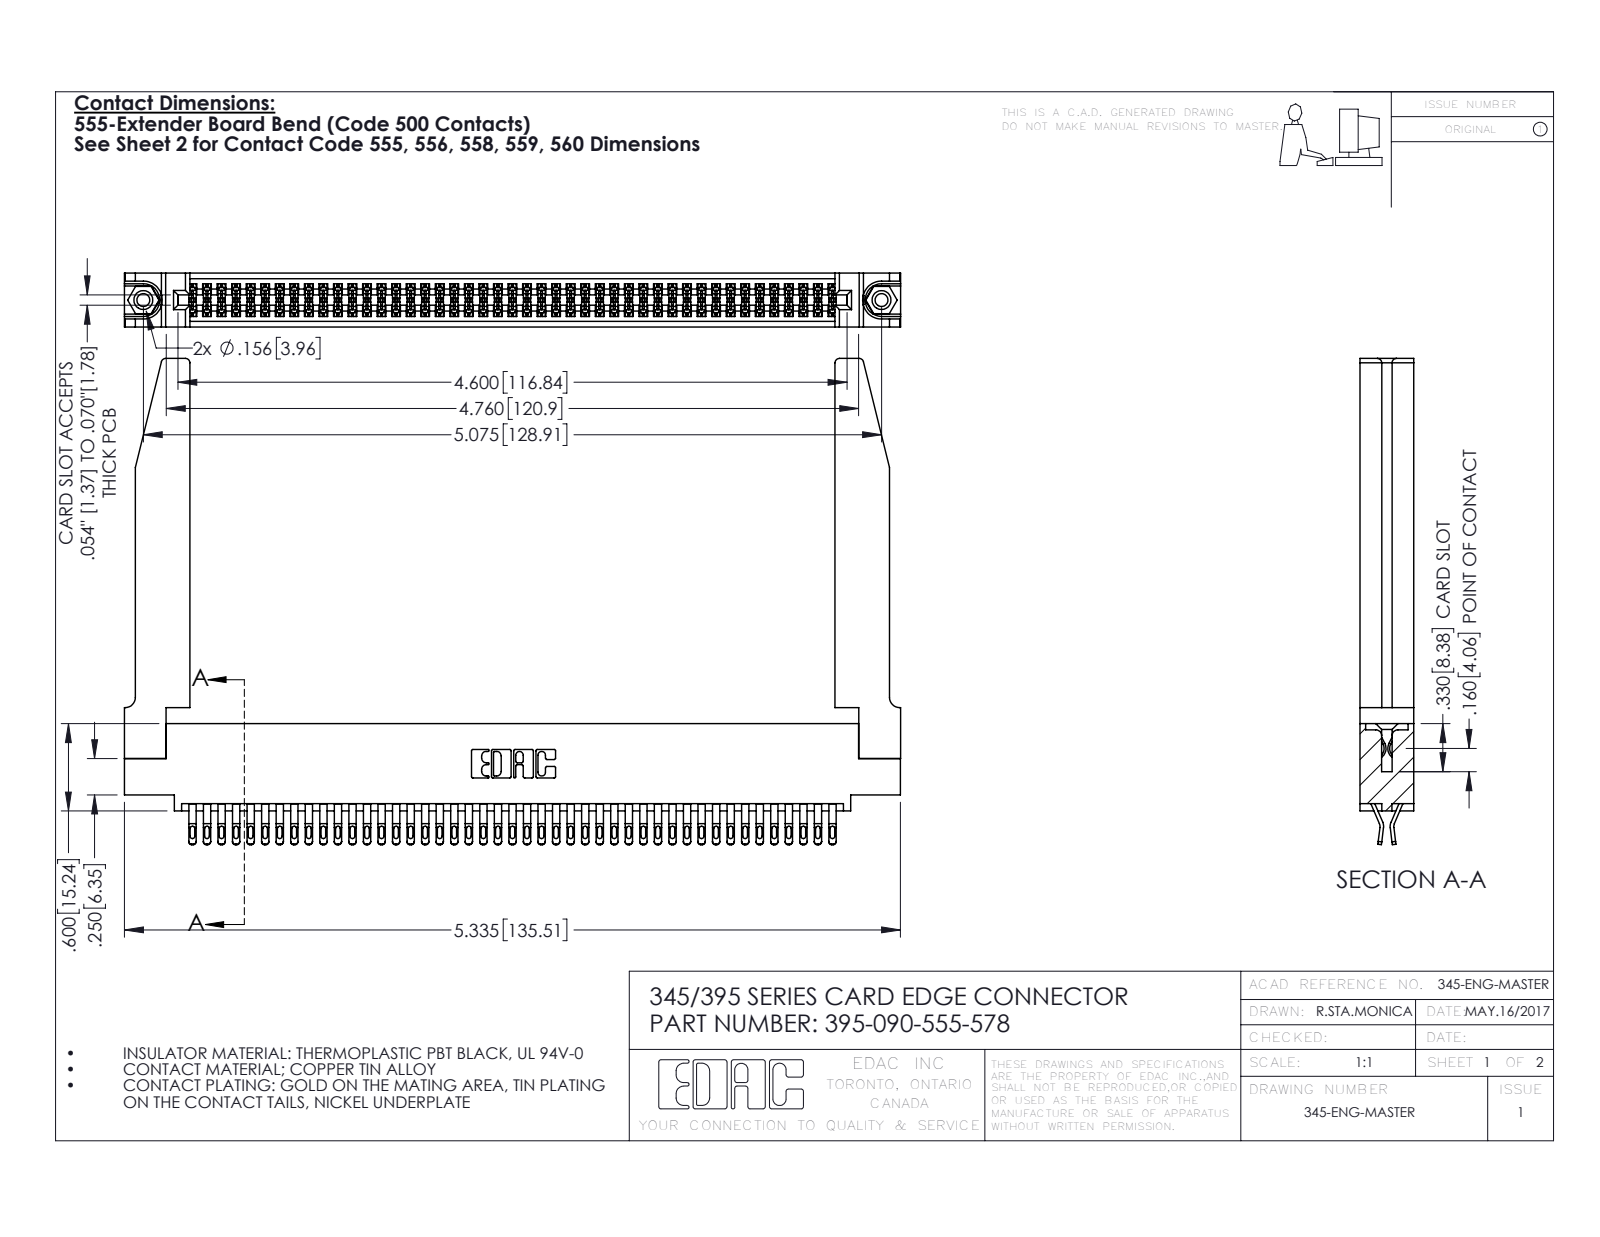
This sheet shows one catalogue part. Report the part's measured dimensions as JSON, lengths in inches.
{"part_name": "345-292-001_555 Tail; 345-220-078_345-220-078; 345-250-001_345-250-001-102; 395-090-555-578 (+1 more)", "step_written_by": "SolidWorks 2016 (CONFIG_CONTROL_DESIGN)", "units": "inches", "bodies": {"solids": 95, "faces": 5404, "planar": 3016, "cylindrical": 2336, "other": 52}, "overall_size": [5.336, 3.342, 0.37], "volume_in3": 1.291, "surface_area_in2": 42.9, "round_holes": [[0.089, 2], [0.125, 2], [0.156, 2], [0.064, 1]], "round_bosses_or_shafts": [[0.155, 2]], "partial_cylinders_radius": [[0.016, 225], [0.02, 180], [0.006, 135], [0.01, 22], [0.03, 8], [0.007, 6], [0.031, 6], [0.026, 3]], "face_to_face_distances": [0.37, 0.072, 0.298, 0.025, 0.2, 0.098, 0.272, 0.225, 0.148, 0.15], "hole_center_spacings": [0.27, 4.839, 5.075]}
